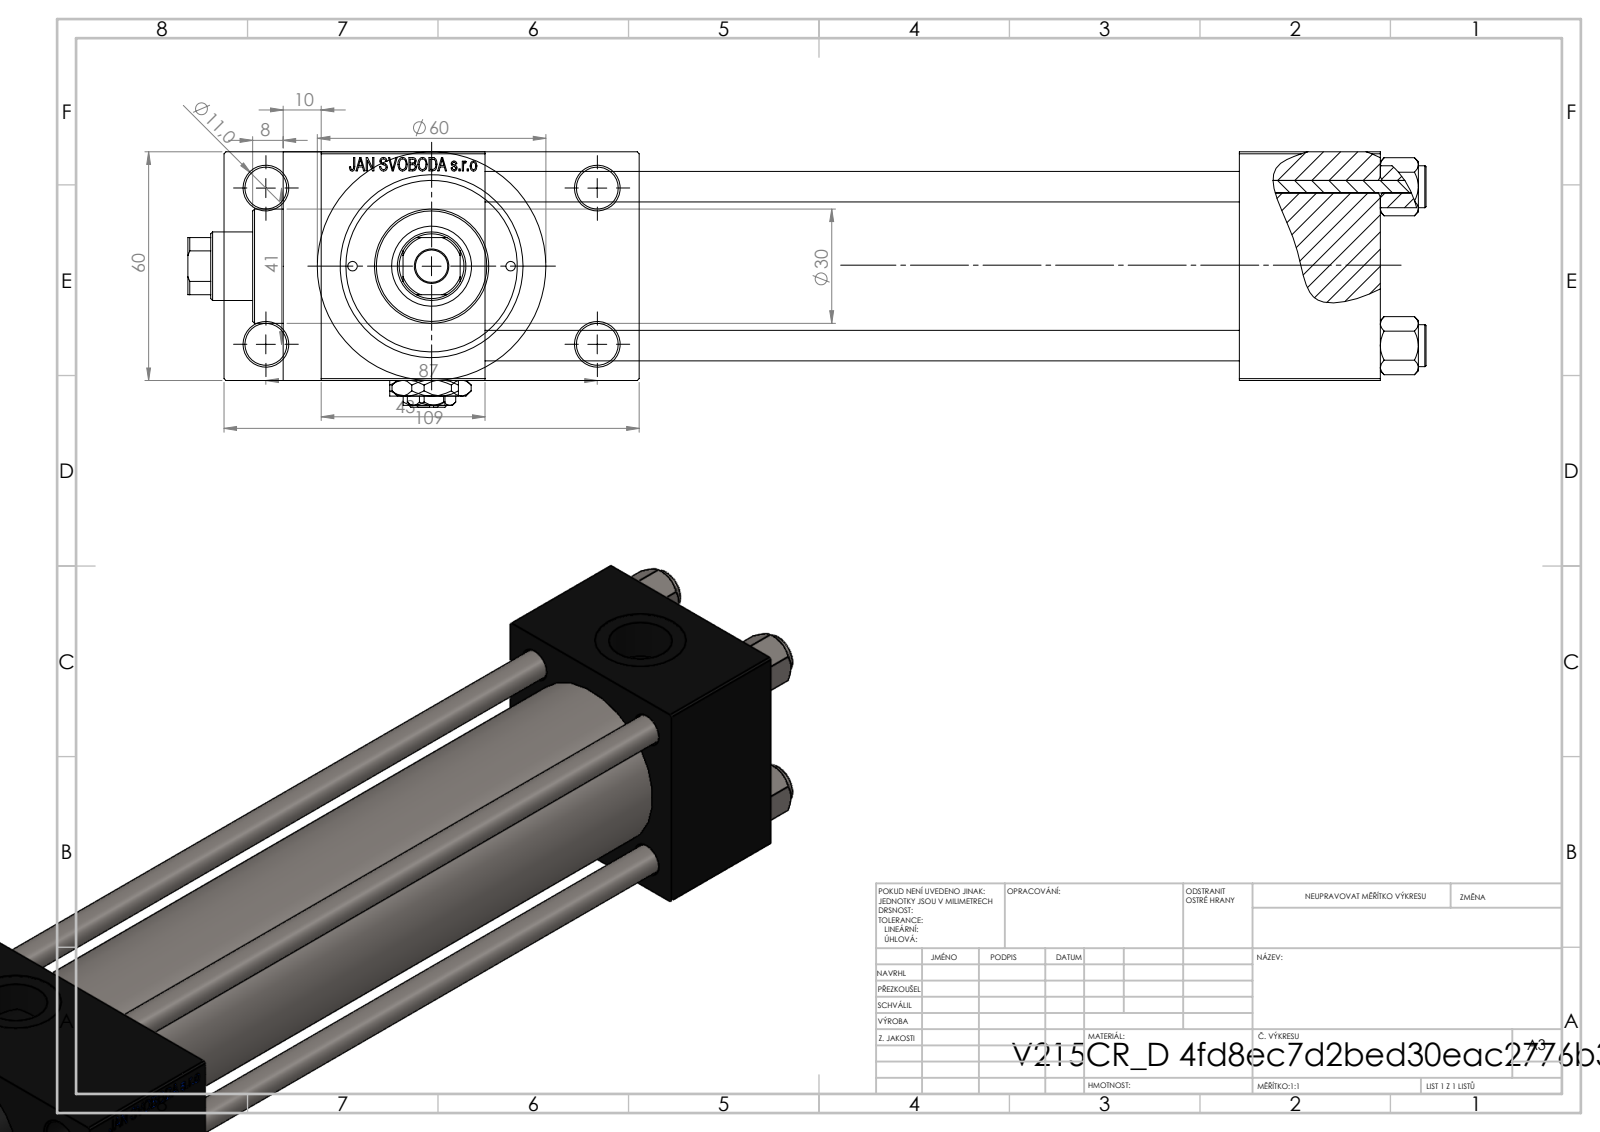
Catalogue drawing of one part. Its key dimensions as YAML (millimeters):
part_name: "V215CR_VCP_D; V215CR_D_Body; V215_VC_A; V215CR_D_TYCINKA (+2 more)"
step_written_by: "SolidWorks 2019 (CONFIG_CONTROL_DESIGN)"
units: millimeters
bodies: {solids: 12, faces: 1161, planar: 524, cylindrical: 97, other: 540}
overall_size: [325, 109, 67]
volume: 637632
surface_area: 181952
round_holes:
  - {diameter: 8, count: 4}
  - {diameter: 11, count: 4}
  - {diameter: 2.5, count: 2}
  - {diameter: 7, count: 2}
  - {diameter: 16.66, count: 2}
  - {diameter: 24, count: 2}
  - {diameter: 8.5, count: 1}
  - {diameter: 18, count: 1}
  - {diameter: 21, count: 1}
  - {diameter: 31, count: 1}
  - {diameter: 40, count: 1}
  - {diameter: 45, count: 1}
round_bosses_or_shafts:
  - {diameter: 11, count: 4}
  - {diameter: 60, count: 1}
  - {diameter: 46, count: 1}
  - {diameter: 30, count: 1}
partial_cylinders:
  - {radius: 8.5, count: 1}
face_to_face_distances: [60, 24.5, 84.5, 198, 37, 235, 43, 278, 241, 109]
hole_center_spacings: [20.85, 22.65, 29.49, 30.62, 41.7, 46.53, 47.15, 48.09]
